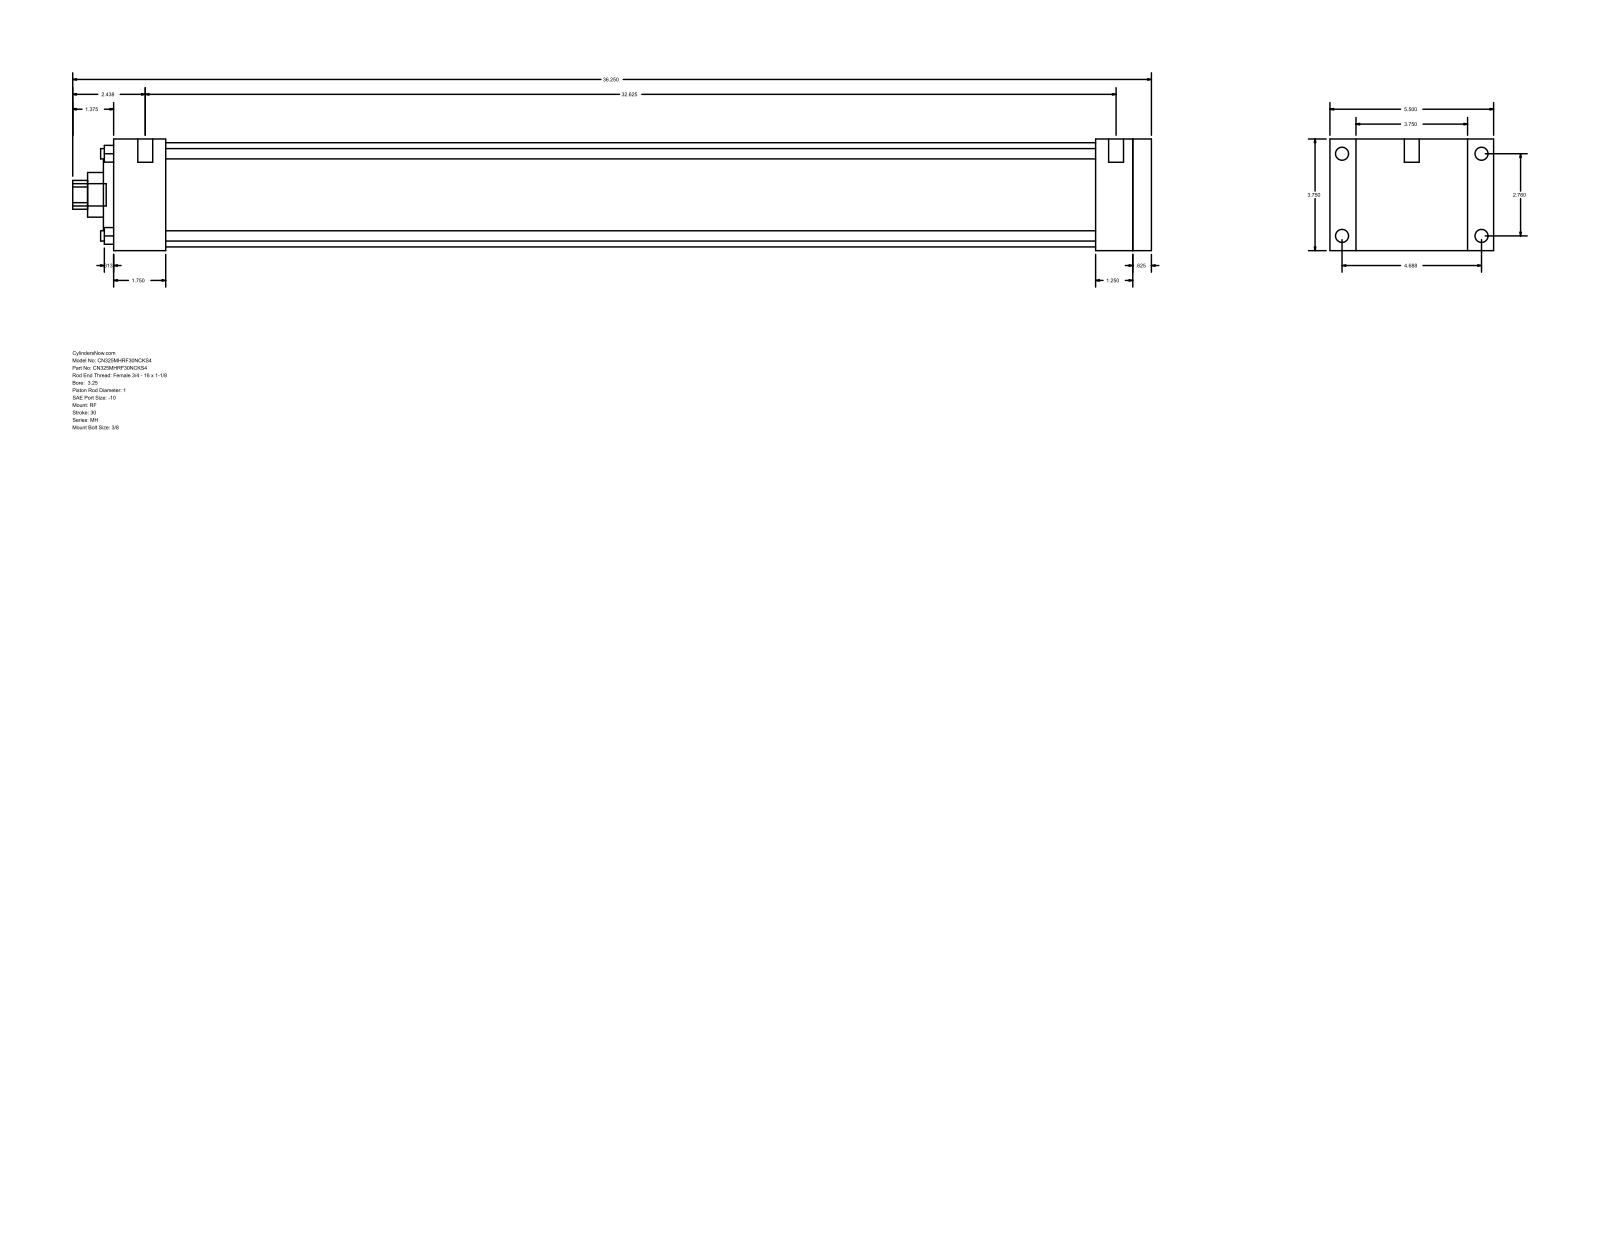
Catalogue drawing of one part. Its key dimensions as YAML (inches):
part_name: "MH_RF__0325_1"
step_written_by: "GSSL Pune (CONFIG_CONTROL_DESIGN)"
units: inches
bodies: {solids: 0, faces: 94, planar: 65, cylindrical: 29, other: 0}
overall_size: [36.25, 5.5, 3.75]
round_holes:
  - {diameter: 0.345, count: 4}
  - {diameter: 1, count: 1}
  - {diameter: 1.5, count: 1}
  - {diameter: 2.375, count: 1}
  - {diameter: 3.5, count: 1}
round_bosses_or_shafts:
  - {diameter: 0.438, count: 4}
  - {diameter: 0.219, count: 4}
  - {diameter: 0.5, count: 2}
  - {diameter: 0.75, count: 1}
partial_cylinders:
  - {radius: 0.484, count: 1}
face_to_face_distances: [3.75, 34.875, 0.625, 34.25, 0.875, 4.625, 1.75, 32.5, 33.125, 33]
hole_center_spacings: [1.952, 2.76, 3.903]
